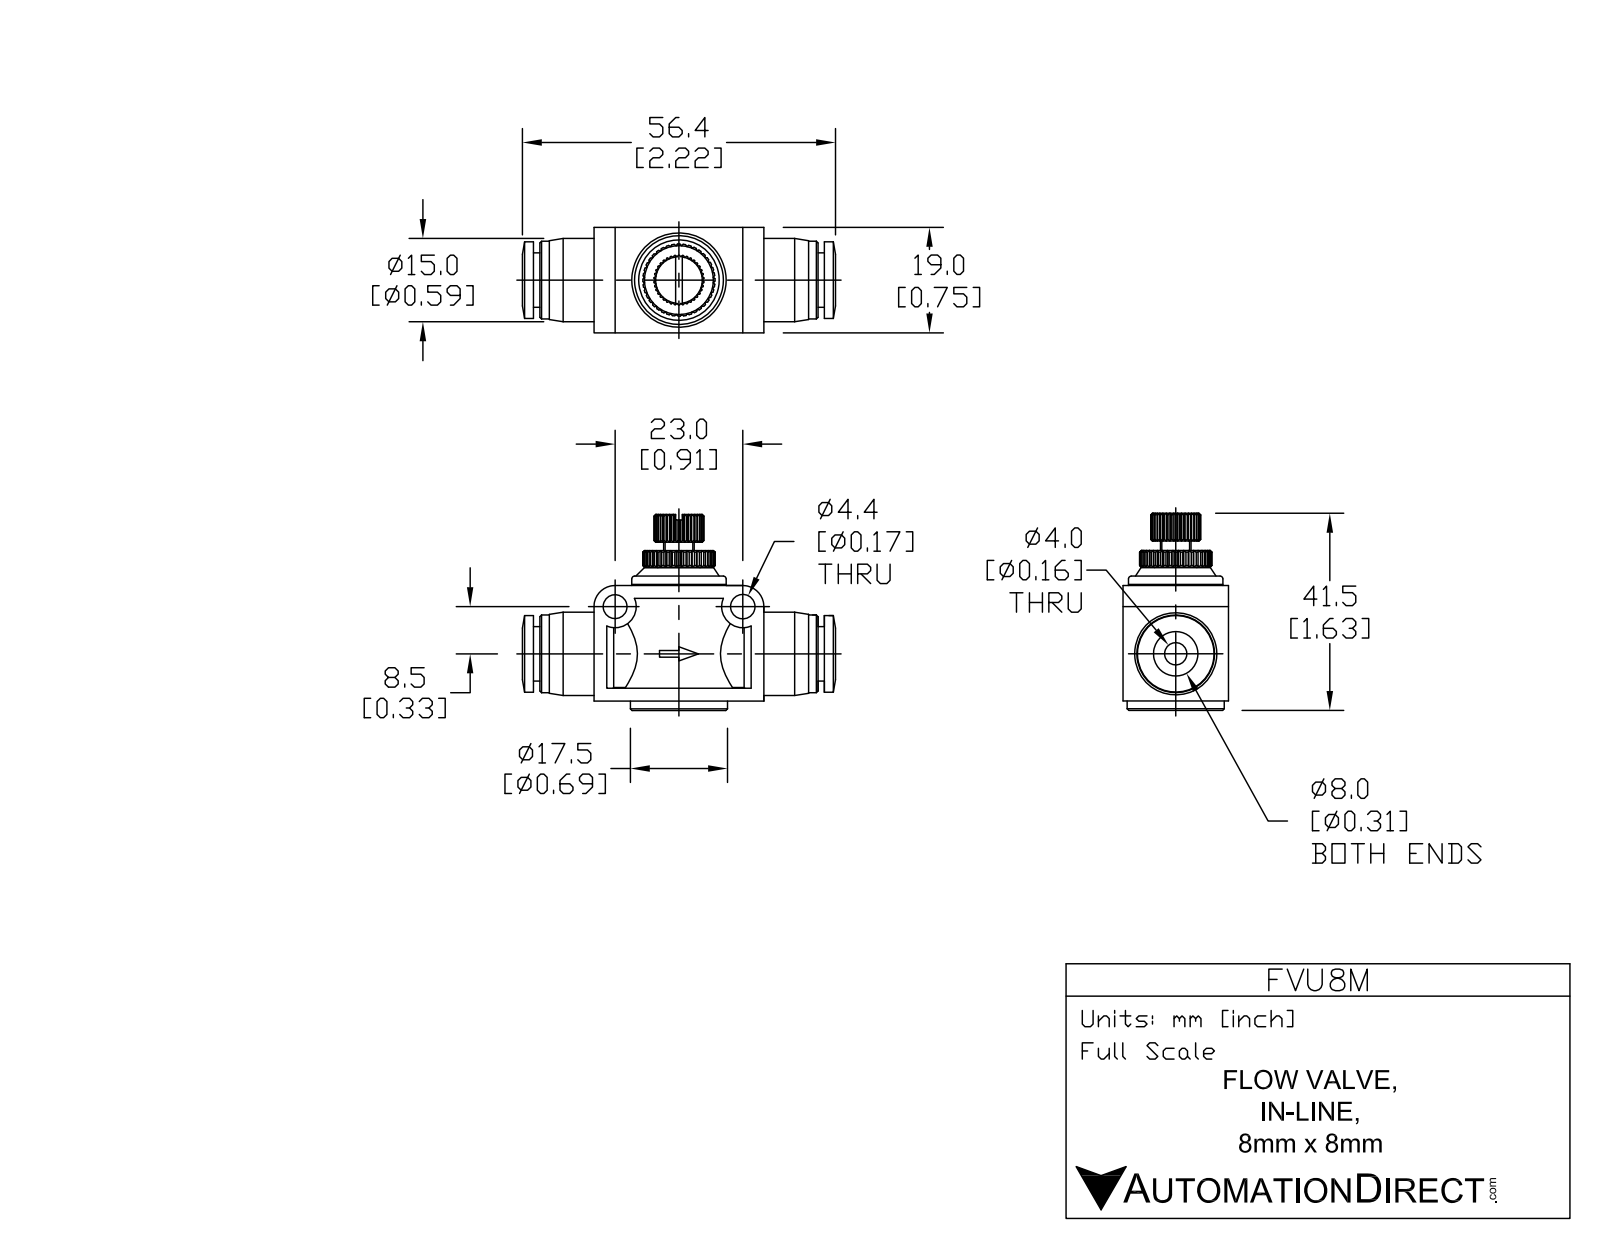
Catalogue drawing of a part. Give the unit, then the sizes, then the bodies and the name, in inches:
Units: inches
Overall size (bounding box): 2.26 × 1.634 × 0.748
Round holes (diameter × count): ⌀0.169 ×2, ⌀0.217 ×1, ⌀0.327 ×1
Round bosses / shafts (diameter × count): ⌀0.689 ×1, ⌀0.669 ×1, ⌀0.591 ×1, ⌀0.551 ×1, ⌀0.543 ×1, ⌀0.386 ×1, ⌀0.299 ×1, ⌀0.217 ×1
Partial cylindrical surfaces — rounded edges, fillets, slot ends (radius × count): R0.15 ×2, R0.177 ×1, R0.246 ×1, R0.256 ×1, R0.384 ×1
Main face-to-face distances: 0.091, 0.748, 0.067, 0.886, 0.157, 0.819, 0.728, 0.74, 0.449, 1.654
Hole centre spacings: 0.906
Volume: 0.826 in³ · Surface area: 12.2 in²
Bodies: 1 solid, 528 faces (215 planar, 130 cylindrical, 183 other)
Part name (STEP PRODUCT): FVU8M
STEP written by: SolidWorks 2015 (AUTOMOTIVE_DESIGN)
